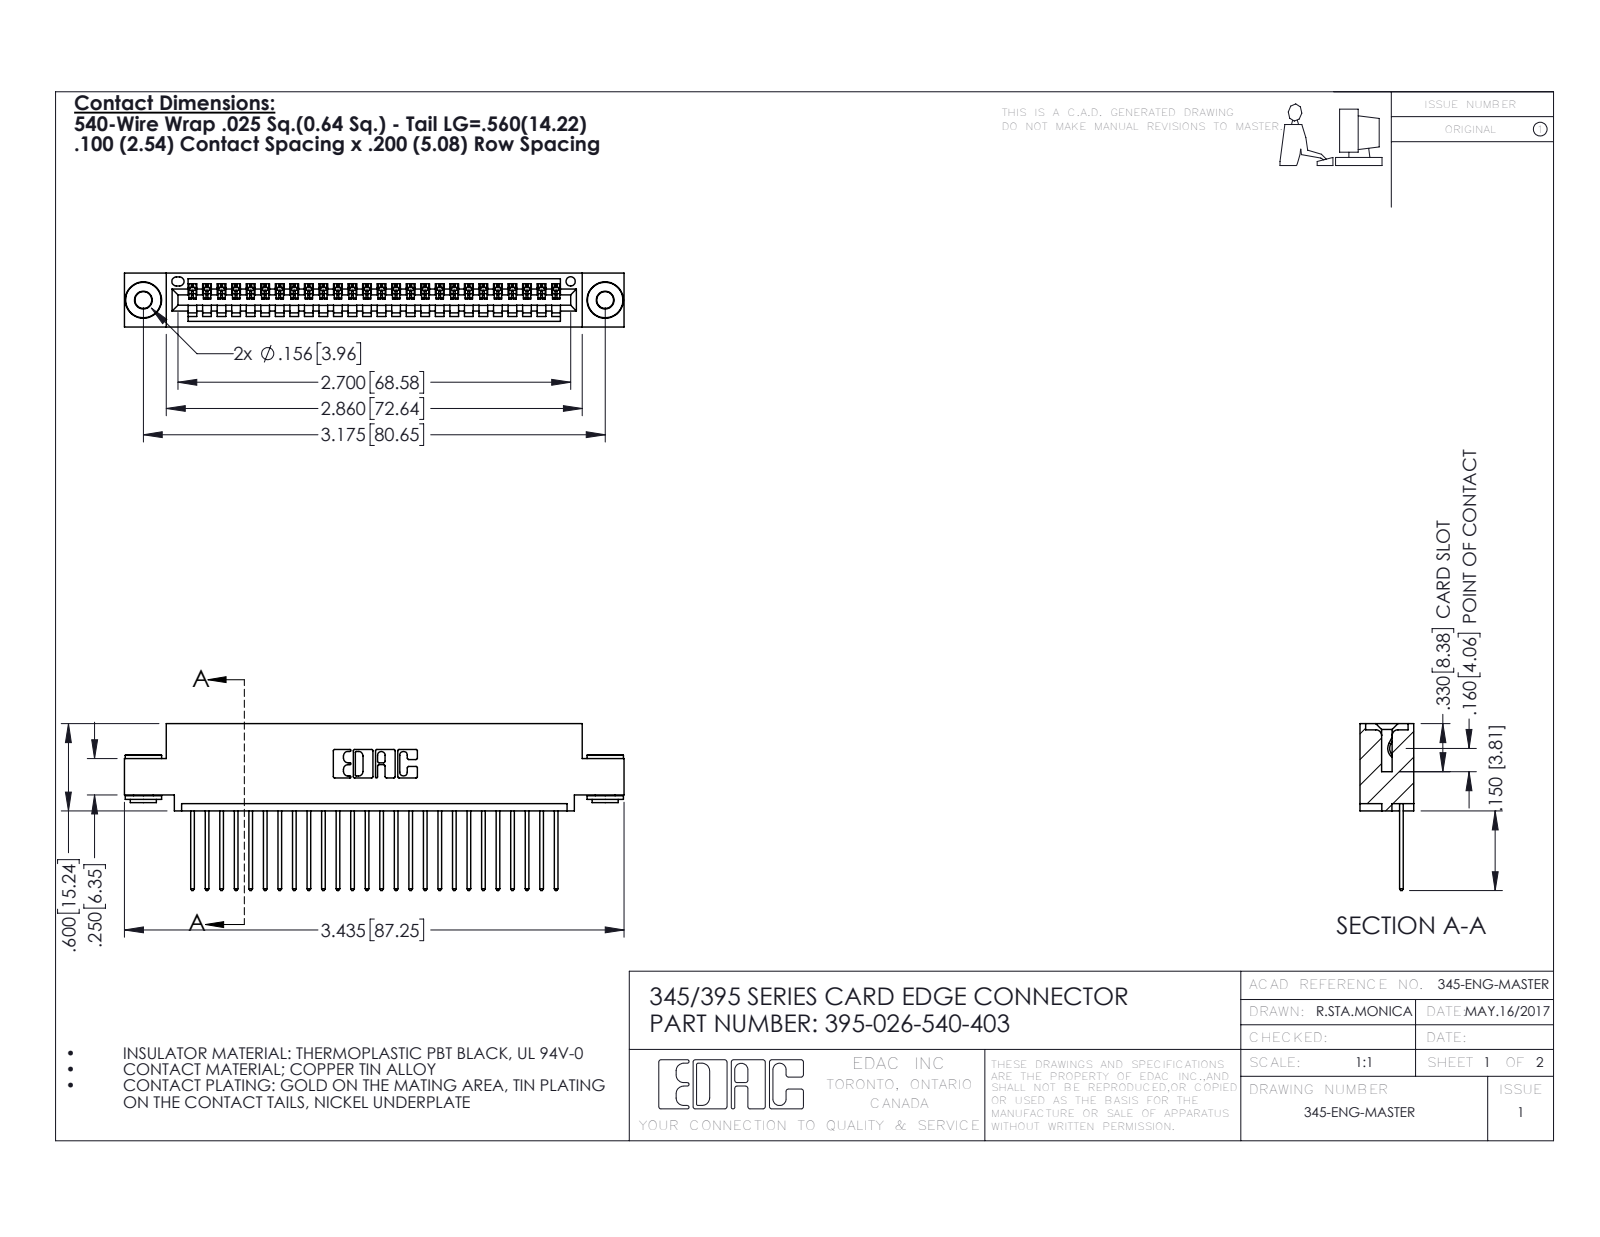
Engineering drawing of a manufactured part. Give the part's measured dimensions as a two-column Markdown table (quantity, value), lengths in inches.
| quantity | value |
| --- | --- |
| part name | 345-292-001_345-293-140; 345 Part_0.110 Offset - 0.156 Dia-TH; 395-026-540-403; 345-250-002_345-250-002-102 |
| STEP written by | SolidWorks 2016 (CONFIG_CONTROL_DESIGN) |
| units | inches |
| bodies | 29 solids, 1676 faces (1134 planar, 534 cylindrical, 8 other) |
| overall size | 3.435 × 1.147 × 0.37 |
| volume | 0.497 in³ |
| surface area | 17.28 in² |
| round holes (diameter × count) | 0.116 × 2, 0.156 × 2, 0.064 × 1 |
| round bosses / shafts (diameter × count) | 0.25 × 2, 0.18 × 2, 0.136 × 2 |
| partial cylindrical surfaces (radius × count) | 0.006 × 52, 0.01 × 52, 0.01 × 22, 0.007 × 6, 0.031 × 6, 0.026 × 3, 0.031 × 2, 0.04 × 2 |
| main face-to-face distances | 0.072, 0.298, 0.37, 0.2, 0.025, 0.098, 0.272, 0.225, 0.149, 0.072 |
| hole center spacings | 0.27, 2.94, 3.175 |
